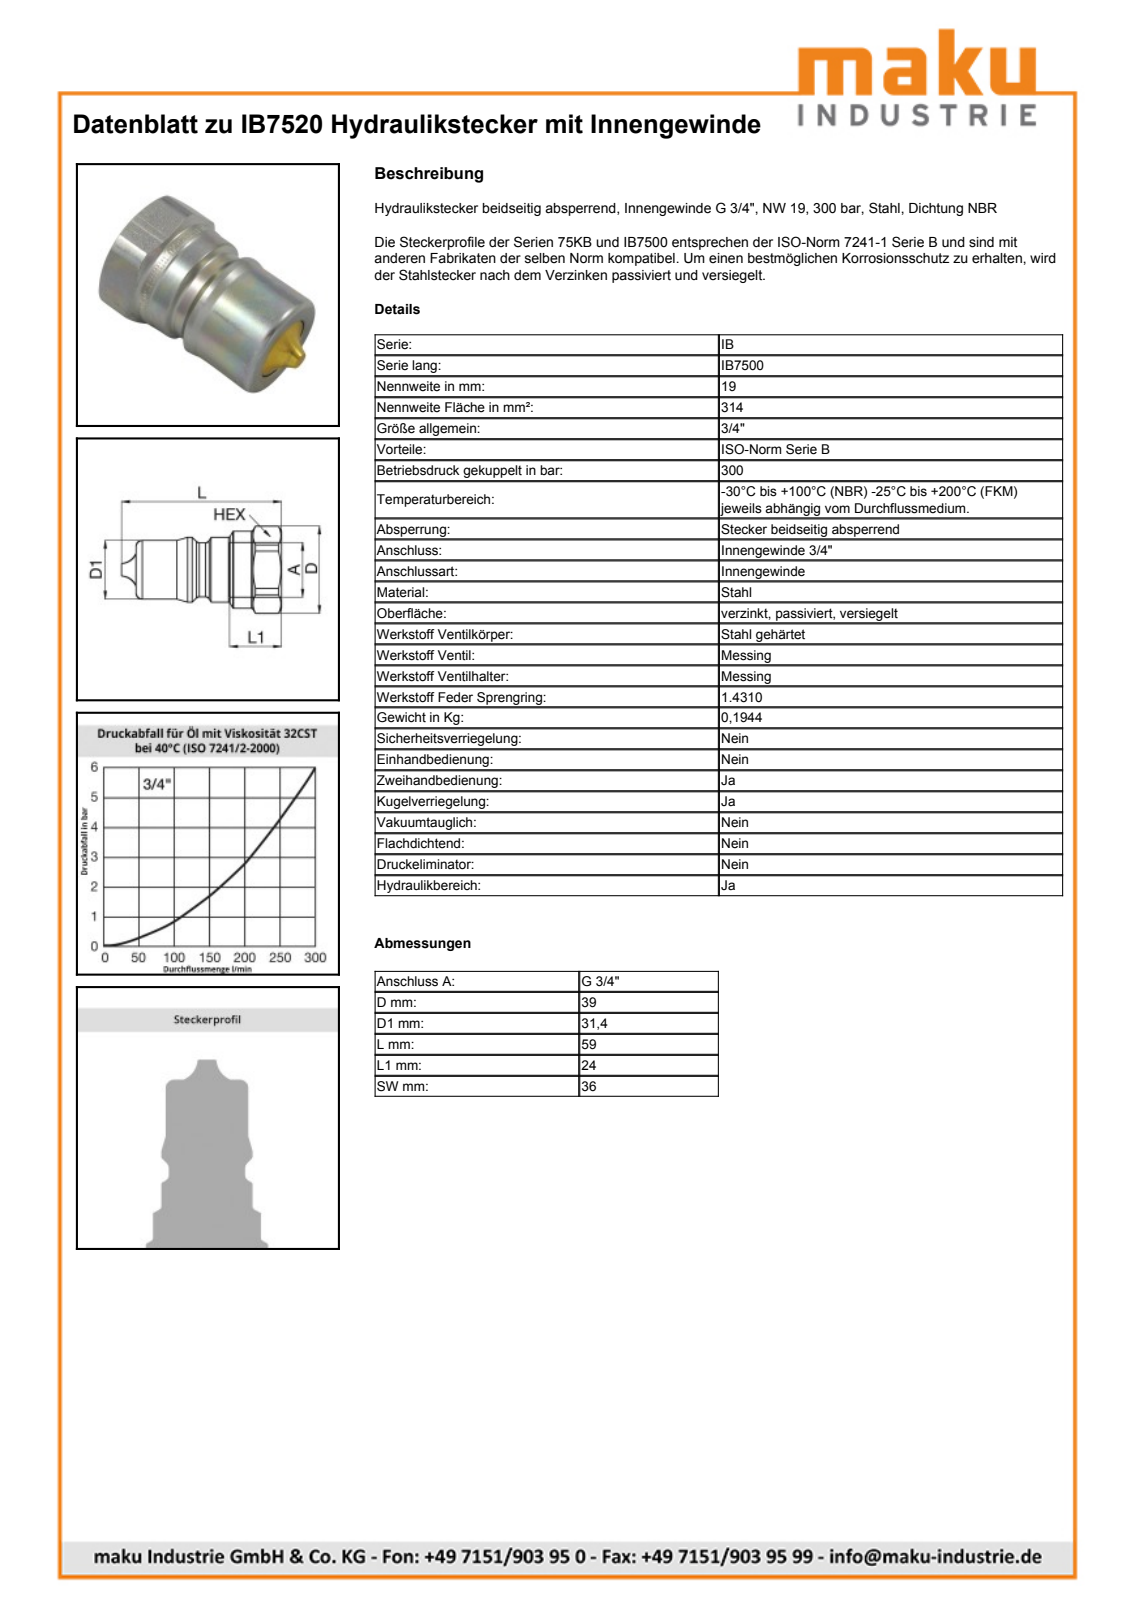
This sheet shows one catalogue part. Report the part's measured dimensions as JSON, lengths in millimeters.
{"part_name": "Part6^IB7520", "step_written_by": "SolidWorks 2009 (AUTOMOTIVE_DESIGN)", "units": "millimeters", "bodies": {"solids": 1, "faces": 80, "planar": 10, "cylindrical": 23, "other": 47}, "overall_size": [59.2, 39, 36], "volume_mm3": 35911, "surface_area_mm2": 9314, "round_holes": [[19, 1], [23.1, 1], [24.12, 1]], "round_bosses_or_shafts": [[33.4, 1], [32.7, 1], [31.4, 1], [28.5, 1]], "partial_cylinders_radius": [[19.5, 1]], "face_to_face_distances": [36, 21.83, 53, 31.17, 59.2, 37.37, 6.2]}
